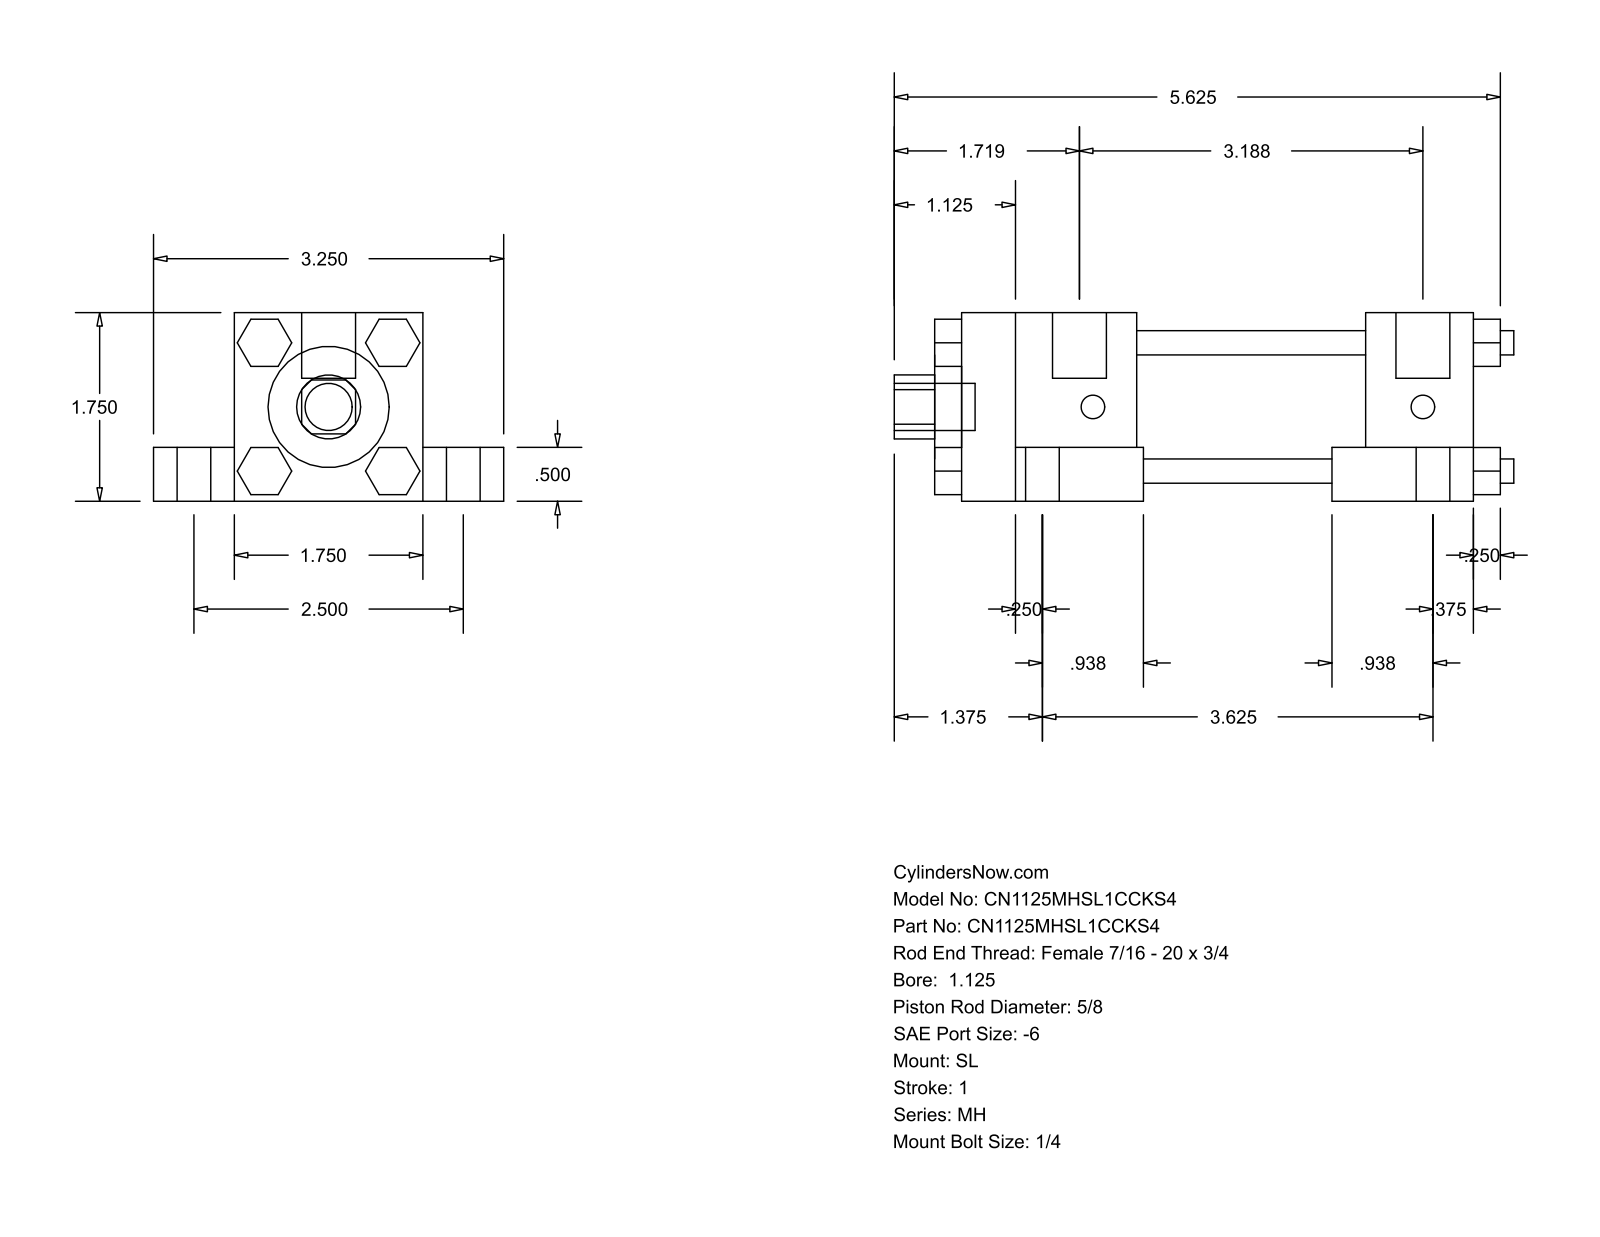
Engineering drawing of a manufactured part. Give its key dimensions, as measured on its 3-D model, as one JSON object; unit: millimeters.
{"part_name": "MH_SL__0112_0.625", "step_written_by": "GSSL Pune (CONFIG_CONTROL_DESIGN)", "units": "millimeters", "bodies": {"solids": 0, "faces": 150, "planar": 114, "cylindrical": 36, "other": 0}, "overall_size": [146.05, 82.55, 44.45], "round_holes": [[15.88, 1], [28.57, 1], [34.92, 1]], "round_bosses_or_shafts": [[14.29, 4], [7.94, 4], [5.71, 4], [5.56, 4], [12.7, 2], [11.11, 1]], "partial_cylinders_radius": [[7.54, 1]], "face_to_face_distances": [44.46, 31.76, 19.04, 12.7, 63.5, 6.35, 127, 11.11, 33.34, 74.62]}
